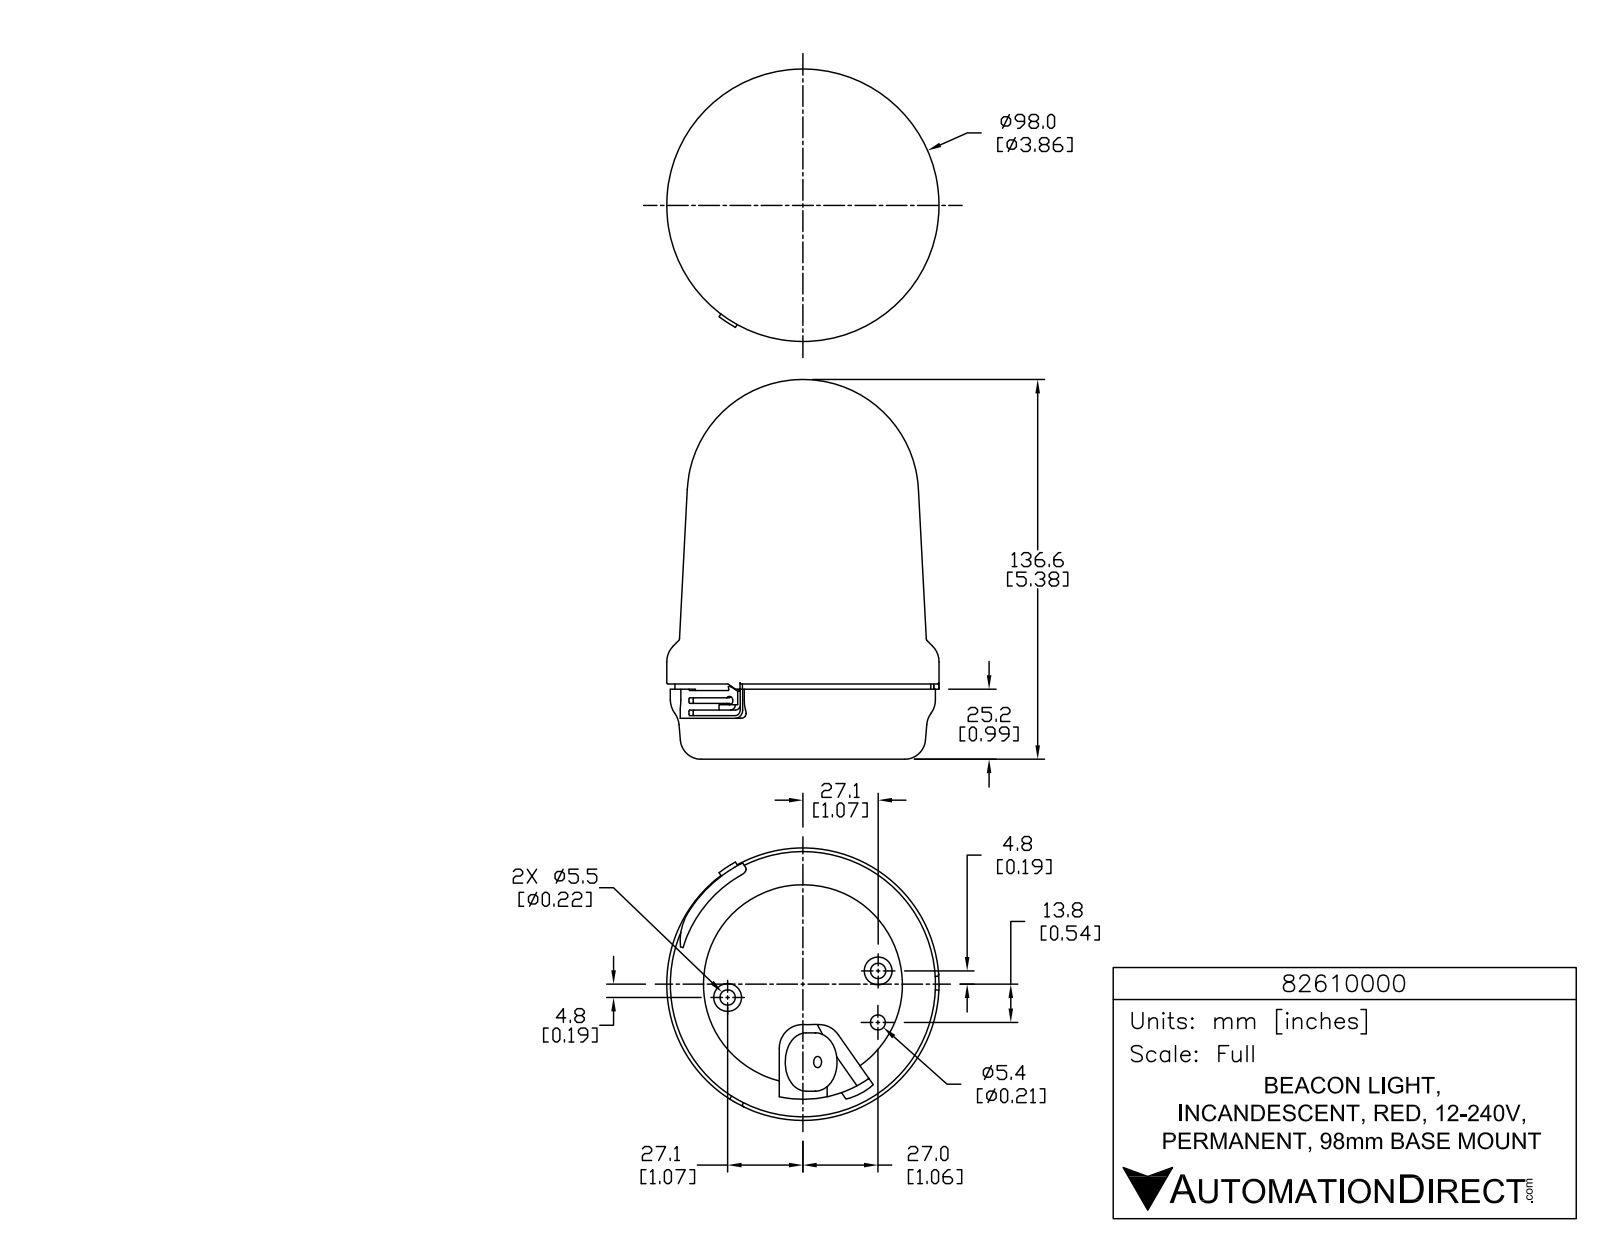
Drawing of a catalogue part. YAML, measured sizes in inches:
part_name: "82610000"
step_written_by: "SolidWorks 2015 (AUTOMOTIVE_DESIGN)"
units: inches
bodies: {solids: 1, faces: 872, planar: 566, cylindrical: 204, other: 102}
overall_size: [5.378, 3.858, 3.858]
volume: 44.69
surface_area: 73.66
round_holes:
  - {diameter: 0.059, count: 3}
  - {diameter: 0.217, count: 2}
  - {diameter: 0.157, count: 1}
  - {diameter: 0.213, count: 1}
  - {diameter: 2.819, count: 1}
round_bosses_or_shafts:
  - {diameter: 0.339, count: 3}
  - {diameter: 0.084, count: 3}
  - {diameter: 0.394, count: 2}
  - {diameter: 3.858, count: 1}
  - {diameter: 3.756, count: 1}
  - {diameter: 3.626, count: 1}
  - {diameter: 0.827, count: 1}
partial_cylinders:
  - {radius: 0.005, count: 9}
  - {radius: 0.005, count: 6}
  - {radius: 0.012, count: 6}
  - {radius: 0.012, count: 6}
  - {radius: 0.012, count: 6}
  - {radius: 0.196, count: 6}
  - {radius: 0.02, count: 5}
  - {radius: 0.039, count: 4}
face_to_face_distances: [1.045, 0.972, 0.073, 0.02, 0.992, 1.065, 0.236, 0.579, 0.559, 0.413]
hole_center_spacings: [1.083, 0.73, 1.193, 2.158, 2.165]
